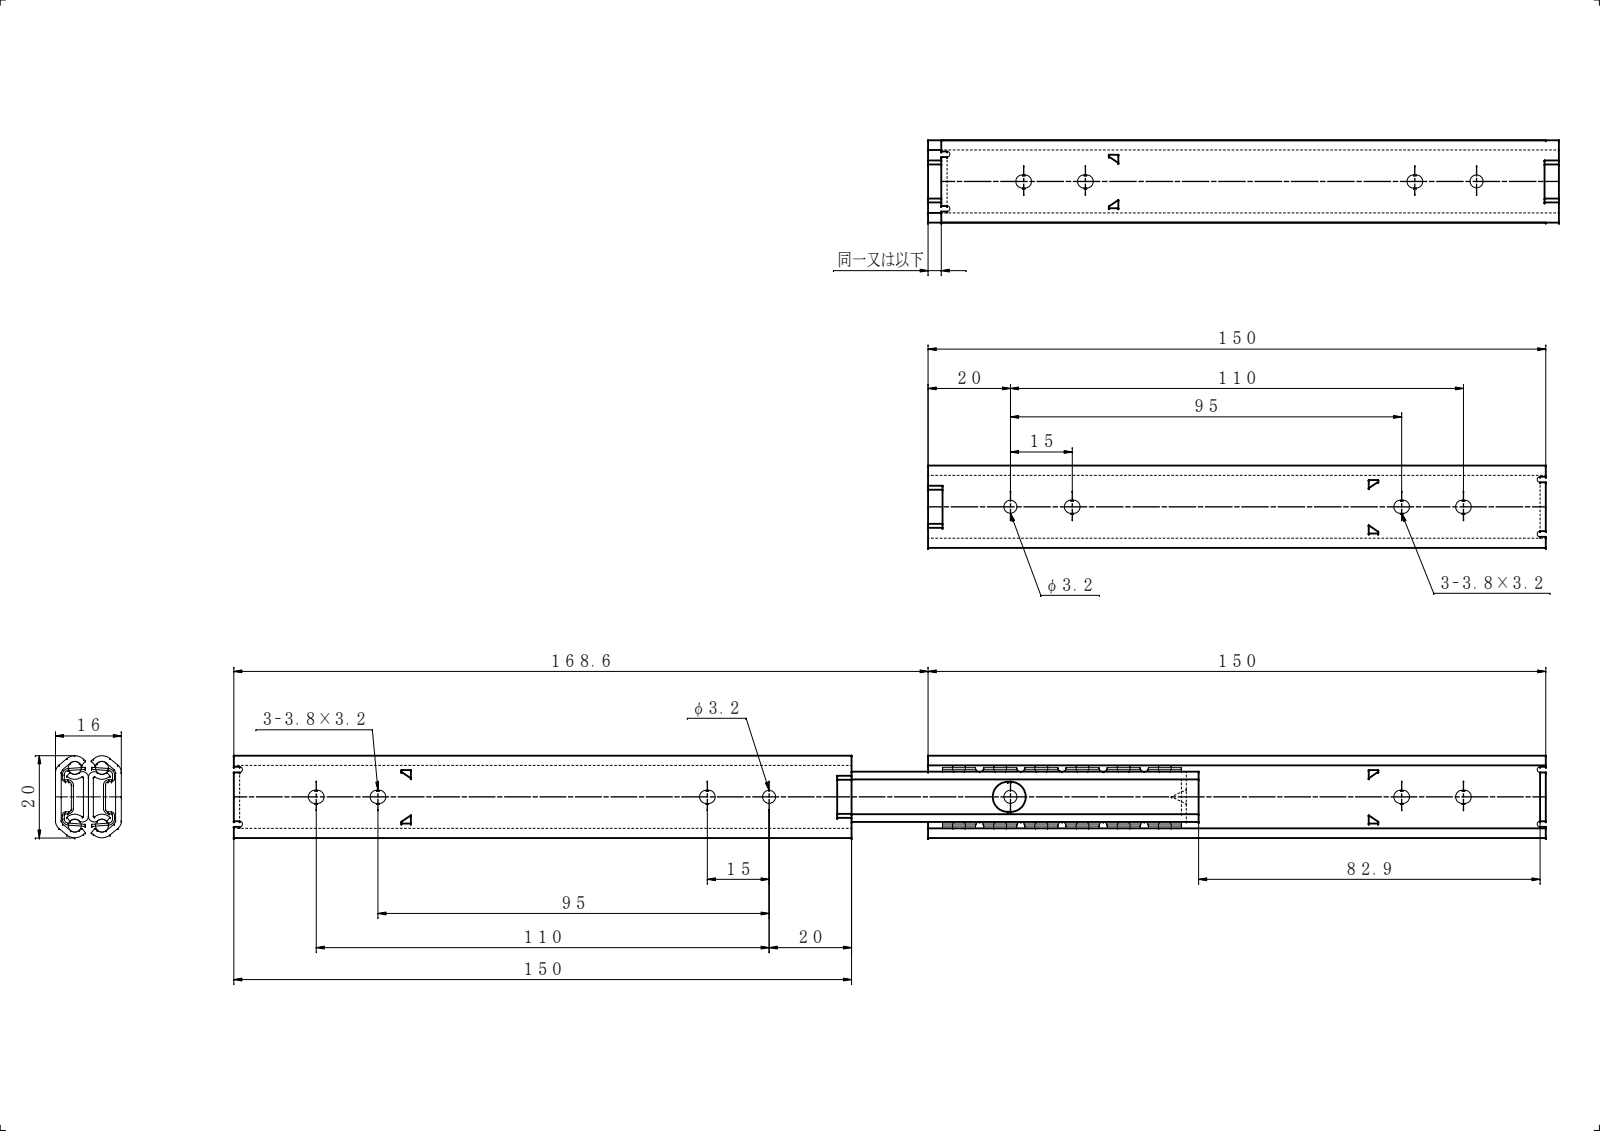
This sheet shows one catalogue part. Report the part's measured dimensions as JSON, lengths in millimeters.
{"part_name": "IM-2031-150; OM-2031-150; 2031-150 AS", "step_written_by": "SolidWorks 2019 (CONFIG_CONTROL_DESIGN)", "units": "millimeters", "bodies": {"solids": 4, "faces": 188, "planar": 98, "cylindrical": 90, "other": 0}, "overall_size": [318.6, 20, 16], "volume_mm3": 18443, "surface_area_mm2": 30084, "round_holes": [[3.2, 2]], "partial_cylinders_radius": [[1.6, 12], [0.3, 8], [1.2, 8], [2.5, 8], [0.23, 4], [1, 4], [1.43, 4], [1.59, 4]], "face_to_face_distances": [1.4, 8, 14.6, 6.6, 1.2, 6.8, 9.2, 5.4, 7.8, 16], "hole_center_spacings": [58.6]}
